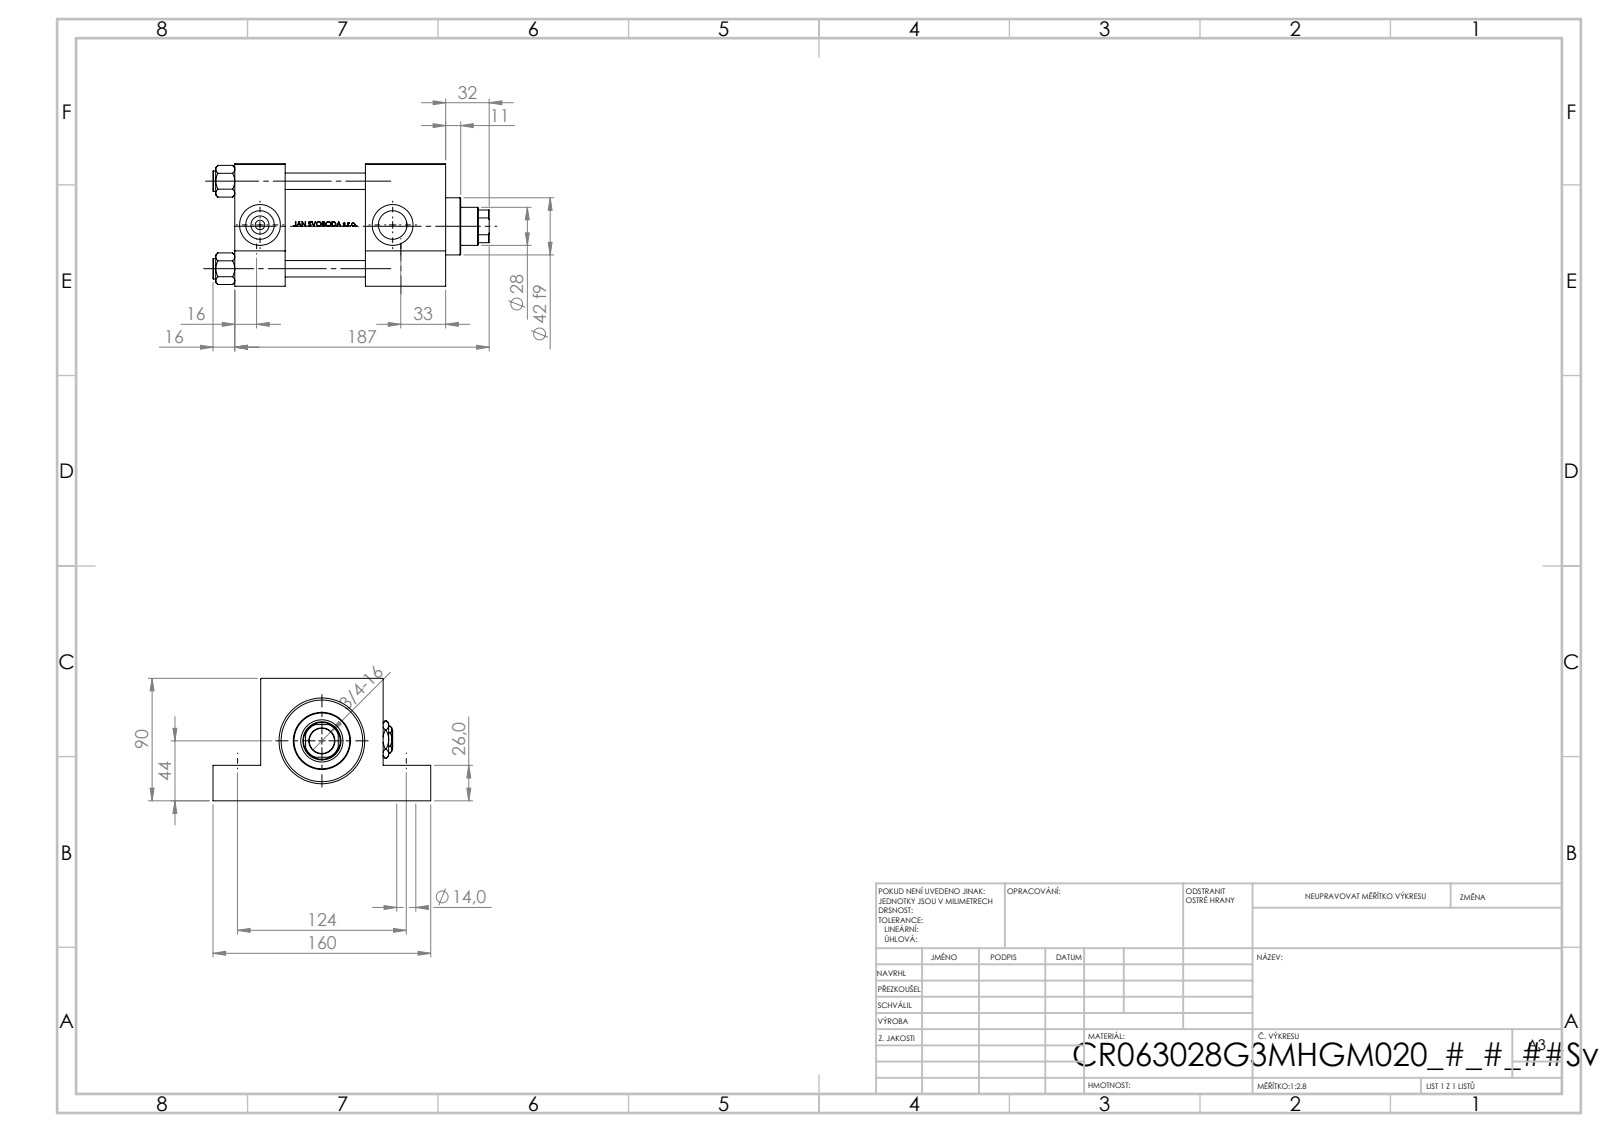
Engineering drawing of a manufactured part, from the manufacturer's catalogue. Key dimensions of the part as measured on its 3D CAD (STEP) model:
Part name (STEP PRODUCT): V215CR_G_Body; V215CR_G_TYCINKA; NUT_M5_G; V215CR_VCP_G (+2 more)
STEP written by: SolidWorks 2019 (CONFIG_CONTROL_DESIGN)
Units: millimetres
Bodies: 13 solids, 1184 faces (478 planar, 132 cylindrical, 574 other)
Overall size (bounding box): 203 × 160 × 90
Volume: 1 110 000 mm³ · Surface area: 204 326 mm²
Round holes (diameter × count): ⌀12 ×4, ⌀14 ×4, ⌀7 ×2, ⌀20.96 ×2, ⌀30 ×2, ⌀18.5 ×1, ⌀28 ×1, ⌀31 ×1, ⌀50 ×1, ⌀60 ×1, ⌀63 ×1
Round bosses / shafts (diameter × count): ⌀15 ×4, ⌀69 ×1, ⌀42 ×1
Partial cylindrical surfaces — rounded edges, fillets, slot ends (radius × count): R13.5 ×1
Main face-to-face distances: 90, 59, 37, 118, 155, 96, 64, 26, 125, 35
Hole centre spacings: 64.3, 44.77, 46.18, 90.93, 106, 124, 163.13, 97.5
